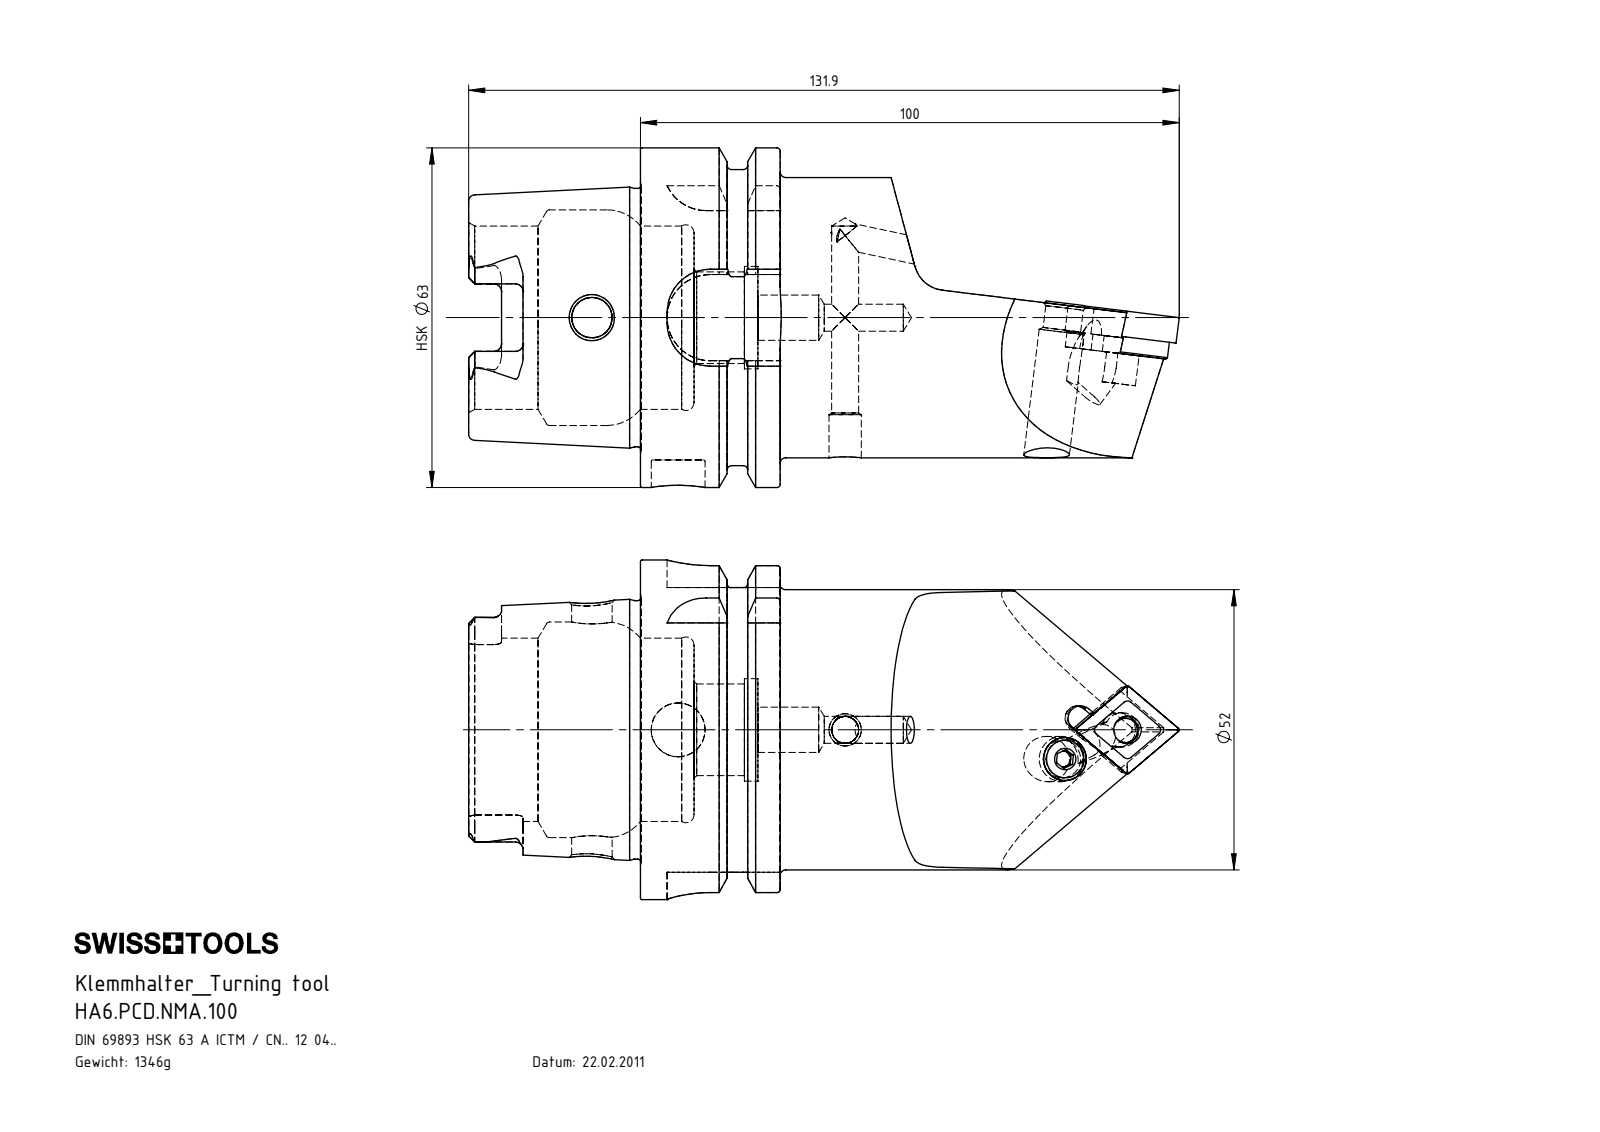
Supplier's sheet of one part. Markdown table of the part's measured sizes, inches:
| quantity | value |
| --- | --- |
| part name | HA6.PCD.NMA.100; WCD-ER1.101.000; WCD-ER4.101.017_A; CNMG120404 (+4 more) |
| STEP written by | SolidWorks 2012 (AUTOMOTIVE_DESIGN) |
| units | inches |
| bodies | 8 solids, 386 faces (121 planar, 109 cylindrical, 156 other) |
| overall size | 5.193 × 2.48 × 2.48 |
| volume | 10.43 in³ |
| surface area | 53.92 in² |
| round holes (diameter × count) | 0.197 × 3, 0.331 × 2, 0.203 × 1, 0.252 × 1, 0.276 × 1, 0.295 × 1, 0.394 × 1, 0.669 × 1, 0.748 × 1, 1.339 × 1, 1.575 × 1 |
| round bosses / shafts (diameter × count) | 2.48 × 1, 2.163 × 1, 2.047 × 1, 1.887 × 1, 0.315 × 1, 0.311 × 1, 0.252 × 1, 0.236 × 1 |
| partial cylindrical surfaces (radius × count) | 0.055 × 6, 0.016 × 4, 0.039 × 4, 0.315 × 4, 0.098 × 2, 0.111 × 2, 0.113 × 2, 0.083 × 1 |
| main face-to-face distances | 1.022, 0.63, 0.392, 1.256, 1.648, 2.278, 2.079, 0.858, 0.467, 0.176 |
| hole center spacings | 0.504, 0.506, 1.22 |
